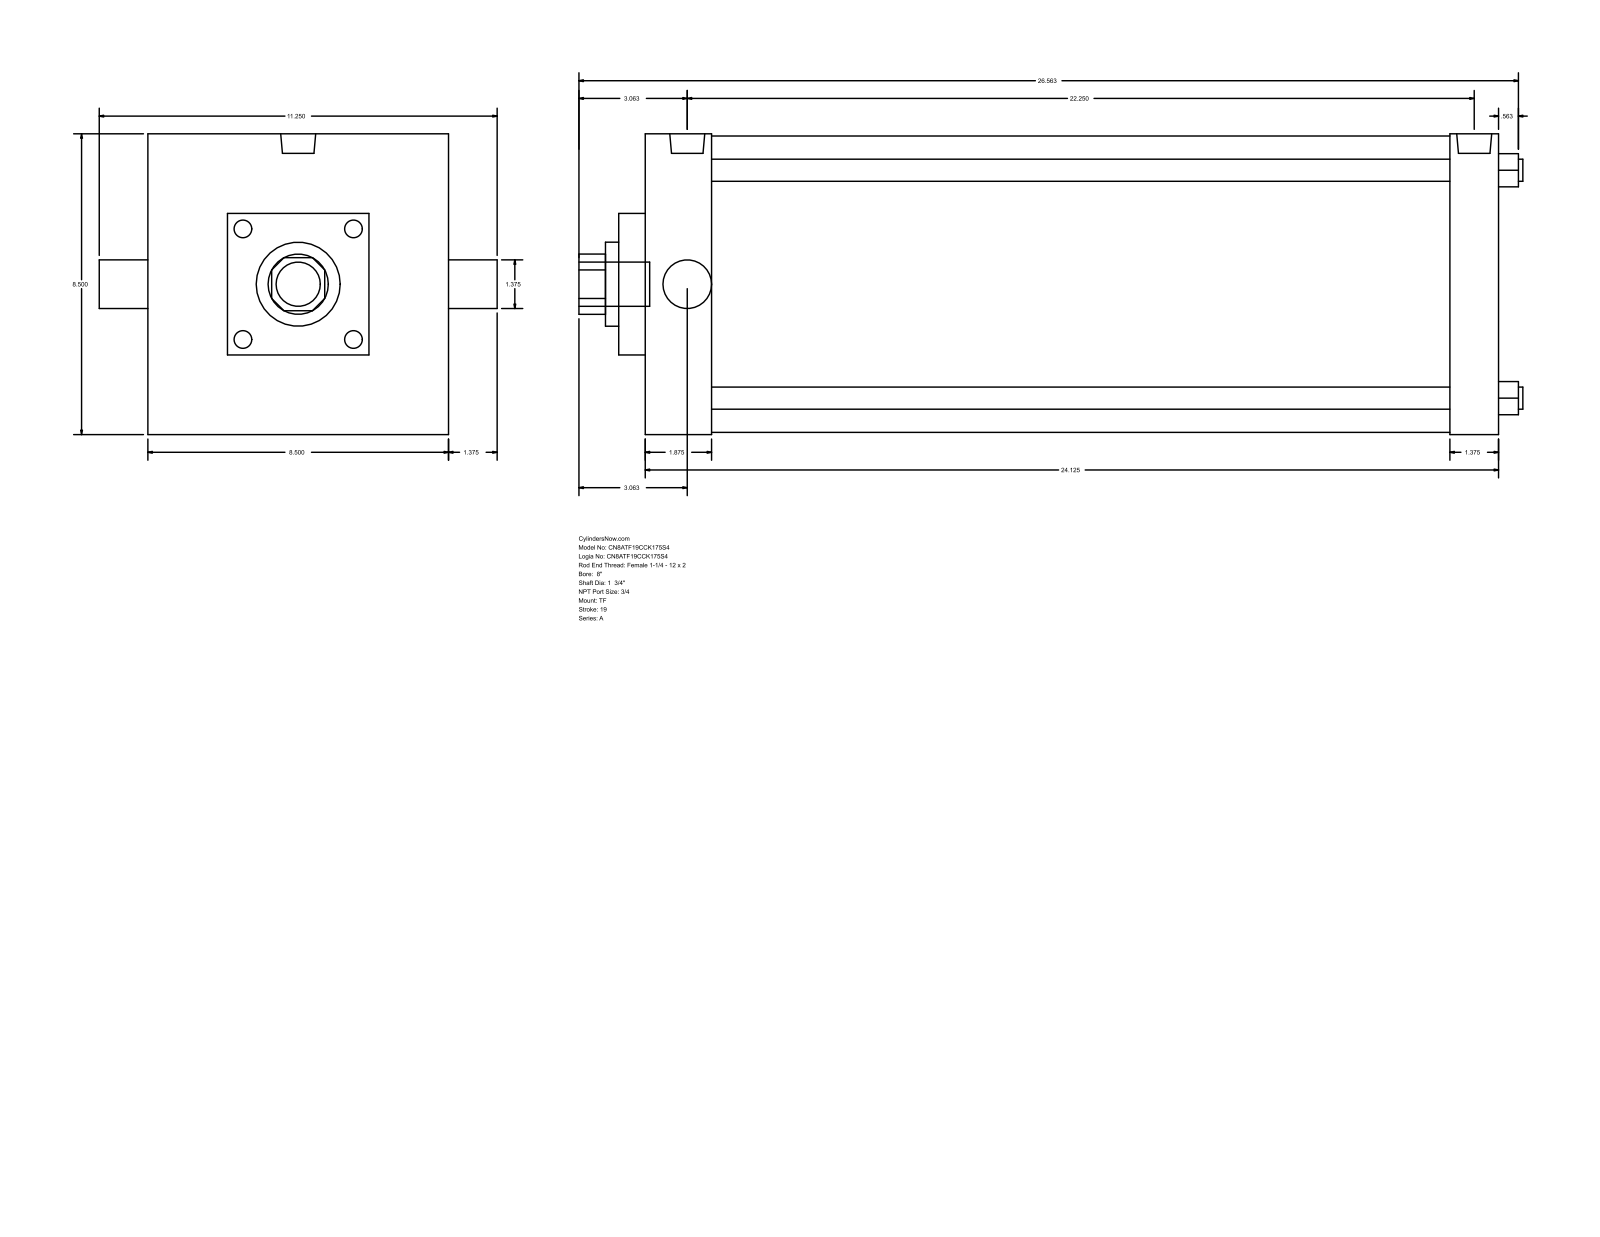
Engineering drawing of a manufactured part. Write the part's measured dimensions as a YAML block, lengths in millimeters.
part_name: "A_TF__0800_1.75"
step_written_by: "GSSL Pune (CONFIG_CONTROL_DESIGN)"
units: millimeters
bodies: {solids: 0, faces: 89, planar: 65, cylindrical: 24, other: 0}
overall_size: [677.86, 285.75, 215.9]
round_holes:
  - {diameter: 15.88, count: 4}
  - {diameter: 34.92, count: 1}
  - {diameter: 44.45, count: 1}
  - {diameter: 60.33, count: 1}
  - {diameter: 212.72, count: 1}
round_bosses_or_shafts:
  - {diameter: 15.08, count: 3}
  - {diameter: 25.12, count: 2}
  - {diameter: 31.75, count: 1}
partial_cylinders:
  - {radius: 21.63, count: 1}
face_to_face_distances: [612.78, 215.9, 34.92, 47.63, 565.15, 577.86, 530.23, 19.05, 57.15, 158.75]
hole_center_spacings: [115.67, 163.58, 231.34]
